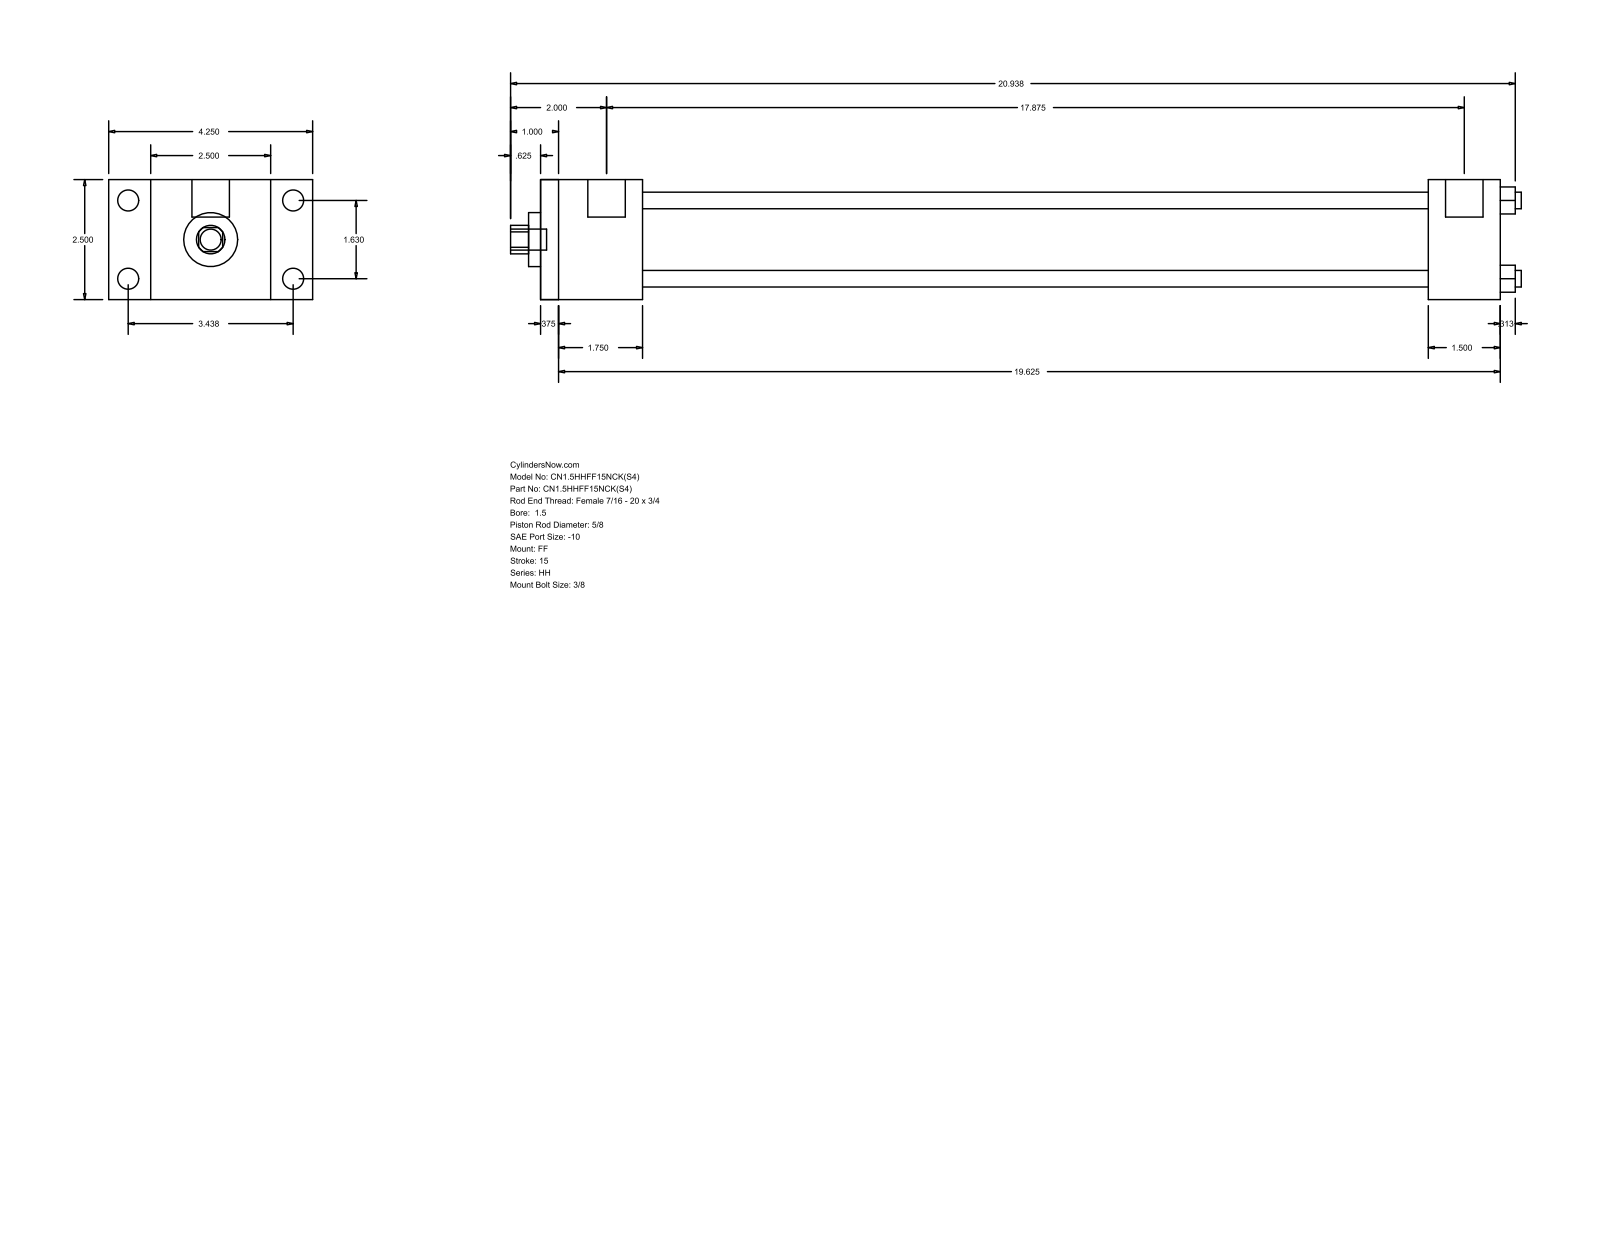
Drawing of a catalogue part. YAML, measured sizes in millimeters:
part_name: "HH_FF__0150_0.625"
step_written_by: "GSSL Pune (CONFIG_CONTROL_DESIGN)"
units: millimeters
bodies: {solids: 0, faces: 92, planar: 64, cylindrical: 28, other: 0}
overall_size: [534.99, 107.95, 63.5]
round_holes:
  - {diameter: 8.76, count: 4}
  - {diameter: 15.88, count: 1}
  - {diameter: 28.57, count: 1}
  - {diameter: 44.45, count: 1}
round_bosses_or_shafts:
  - {diameter: 11.13, count: 4}
  - {diameter: 5.56, count: 4}
  - {diameter: 19.84, count: 2}
  - {diameter: 11.11, count: 1}
partial_cylinders:
  - {radius: 7.54, count: 1}
face_to_face_distances: [63.5, 508, 9.52, 498.48, 53.97, 44.45, 454.03, 469.89, 460.37, 415.92]
hole_center_spacings: [29.27, 41.4, 58.55]
